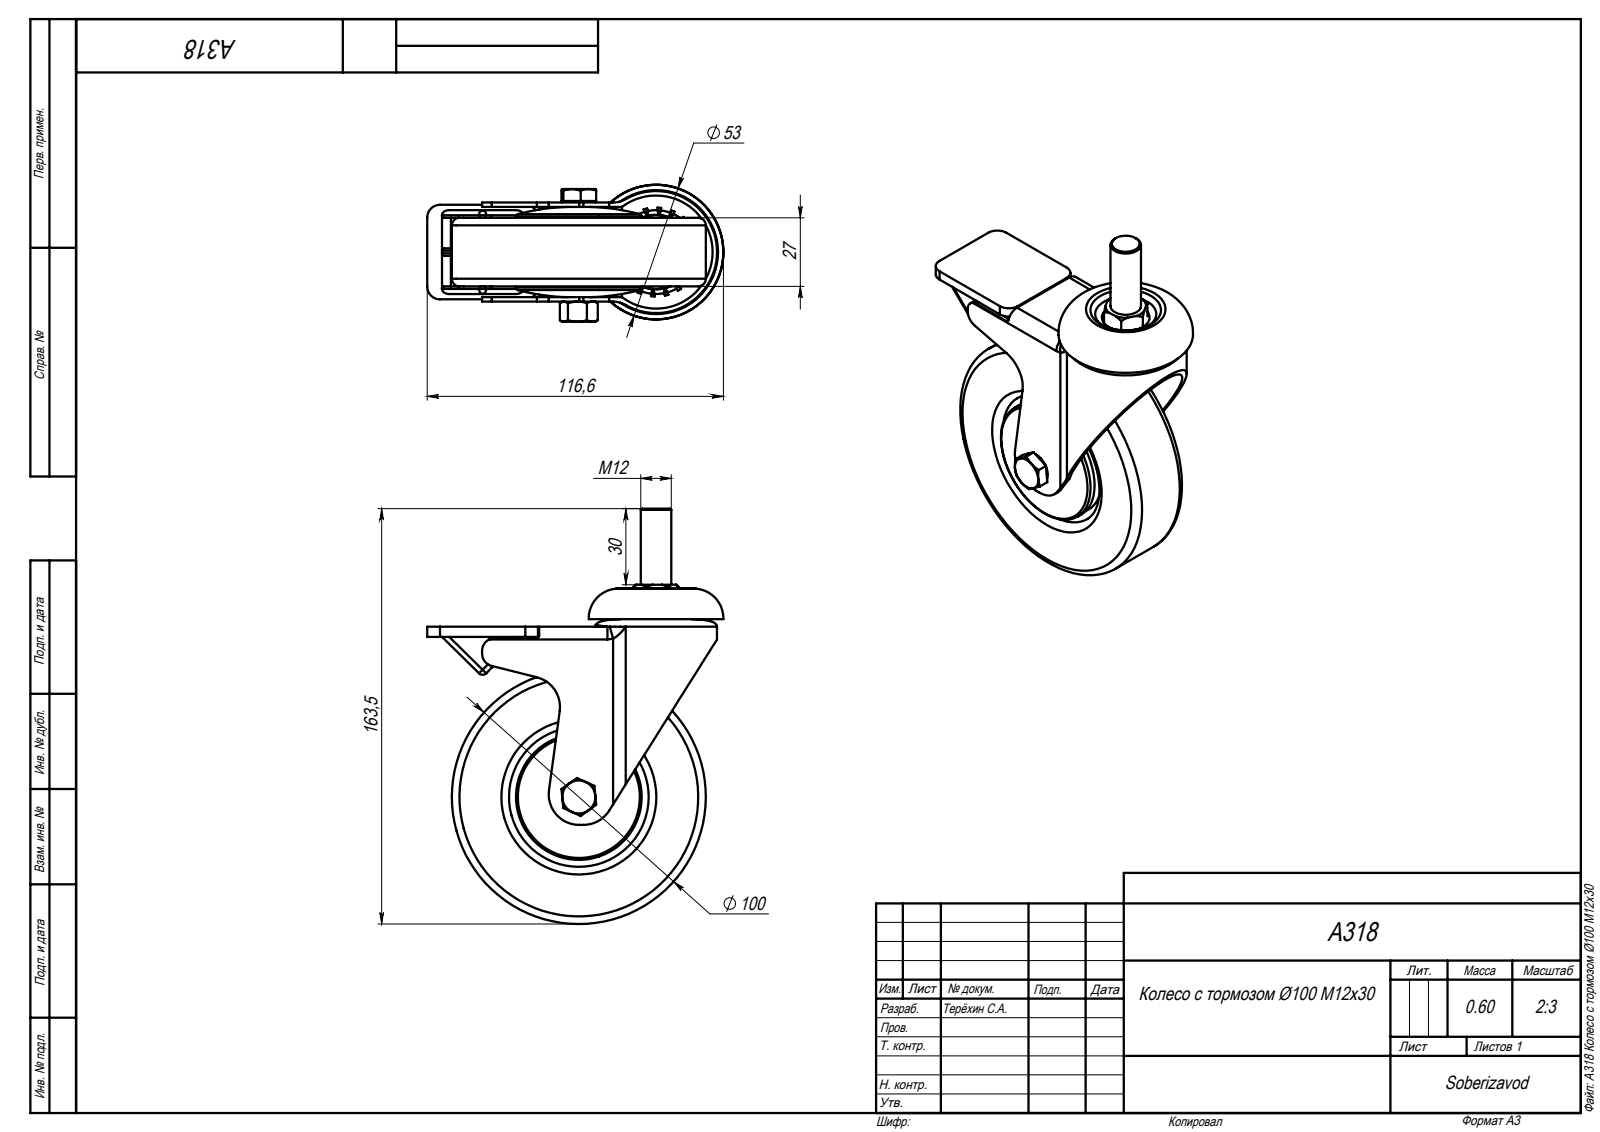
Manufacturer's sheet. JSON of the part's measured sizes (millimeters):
{"part_name": "A318 Колесо с тормозом Ø100 М12х30_00; hex bolt gradeab_din_DIN EN 24014 - M8 x 45 x 22-N; Сборка1; Дно_00 (+8 more)", "step_written_by": "SolidWorks 2024 (AUTOMOTIVE_DESIGN)", "units": "millimeters", "bodies": {"solids": 11, "faces": 359, "planar": 150, "cylindrical": 85, "other": 124}, "overall_size": [163.5, 129.91, 68.71], "volume_mm3": 221670, "surface_area_mm2": 77852, "round_holes": [[2, 1], [6.8, 1], [8, 1], [10, 1], [45.5, 1]], "round_bosses_or_shafts": [[100, 1], [49.5, 1], [13, 1], [12, 1]], "partial_cylinders_radius": [[1, 4], [12, 3], [0.5, 2], [1.5, 2], [2, 2], [7.5, 2], [10, 2], [1.86, 1]], "face_to_face_distances": [2, 4.7, 29.7, 6.7, 31.7, 36.4, 25, 12.7, 25.7, 10.7], "hole_center_spacings": [65.1]}
